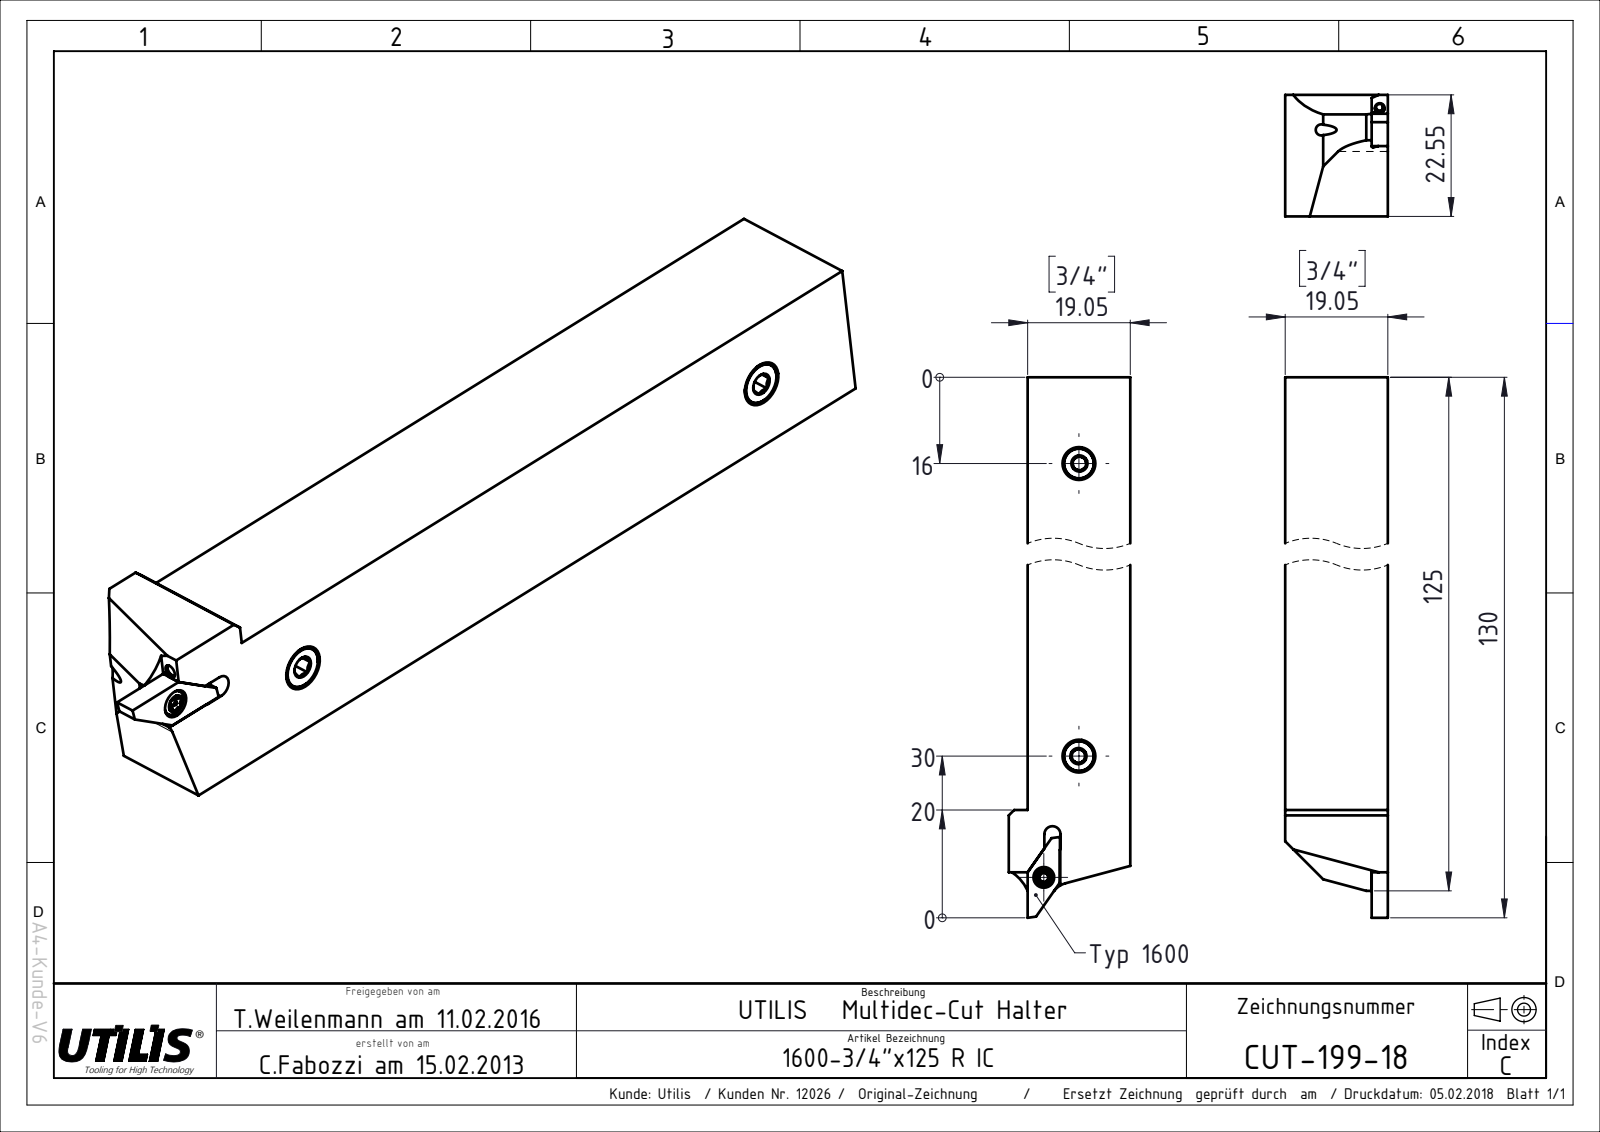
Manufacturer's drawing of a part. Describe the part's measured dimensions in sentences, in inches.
The part is named "CUT-199-18". Its 3-D file was written by "SolidWorks 2017 (AUTOMOTIVE_DESIGN)". It is 1 solid with 46 faces: 37 planar, 6 cylindrical and 3 other. Overall it measures 5.118 by 0.888 by 0.75 inches. Its volume is 2.704 cubic inches and its surface area 15.74 square inches. Partial cylindrical surfaces (rounded edges, fillets, slot ends): 2 of radius 0.059, 1 of radius 0.01, 1 of radius 0.157. The main face-to-face distances are 0.75, 0.888, 0.138, 4.331, 0.118, 0.236, 0.632, 0.514, 0.374, 0.455.
